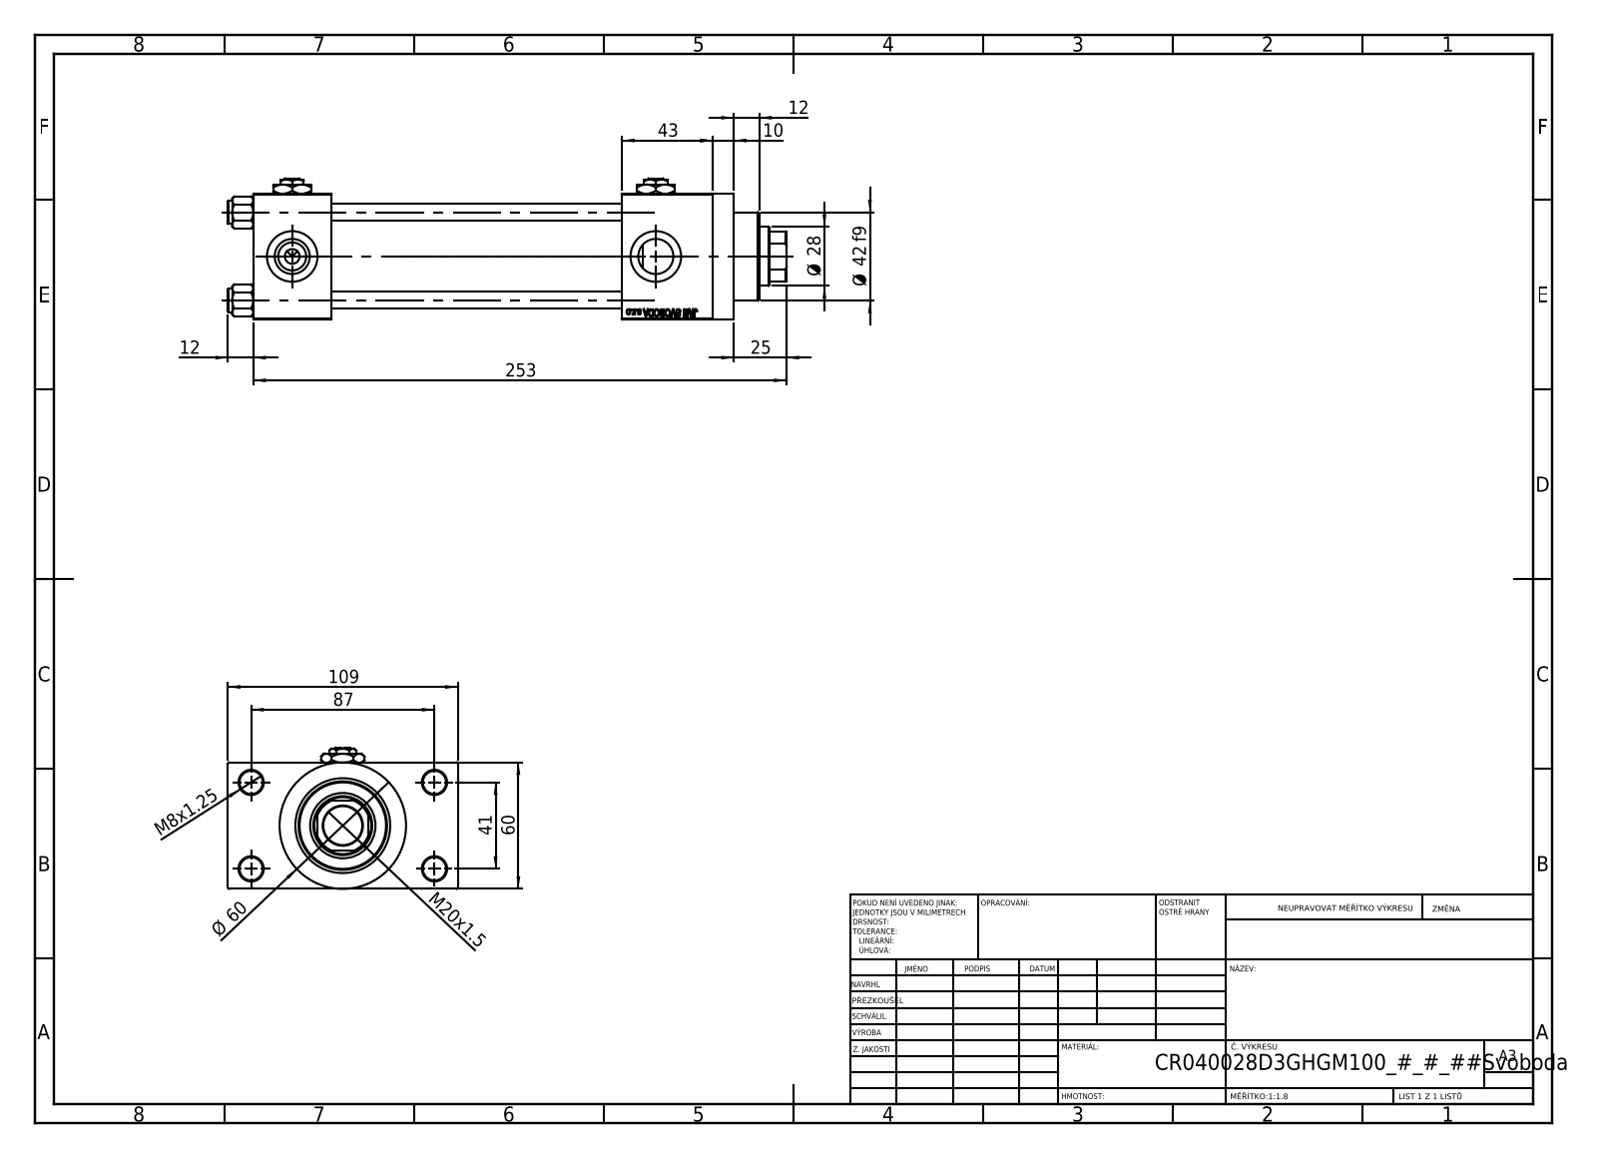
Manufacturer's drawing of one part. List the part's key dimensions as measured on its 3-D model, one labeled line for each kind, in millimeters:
Part name (STEP PRODUCT): NUT_M5_D; Zatka_pro_OIL_PORT; V215CR_VCP_D; V215CR_D_Body (+2 more)
STEP written by: SolidWorks 2019 (CONFIG_CONTROL_DESIGN)
Units: millimetres
Bodies: 13 solids, 1205 faces (546 planar, 99 cylindrical, 560 other)
Overall size (bounding box): 265 × 109 × 67
Volume: 624 458 mm³ · Surface area: 168 445 mm²
Round holes (diameter × count): ⌀8 ×4, ⌀11 ×4, ⌀16.66 ×4, ⌀24 ×4, ⌀7 ×3, ⌀18.5 ×1, ⌀28 ×1, ⌀31 ×1, ⌀40 ×1, ⌀45 ×1
Round bosses / shafts (diameter × count): ⌀11 ×4, ⌀60 ×1, ⌀46 ×1, ⌀42 ×1
Partial cylindrical surfaces — rounded edges, fillets, slot ends (radius × count): R13.5 ×1
Main face-to-face distances: 60, 24.5, 138, 84.5, 37, 175, 218, 181, 43, 109
Hole centre spacings: 22.65, 29.49, 41.7, 47.15, 48.09, 64.35, 76.49, 41
